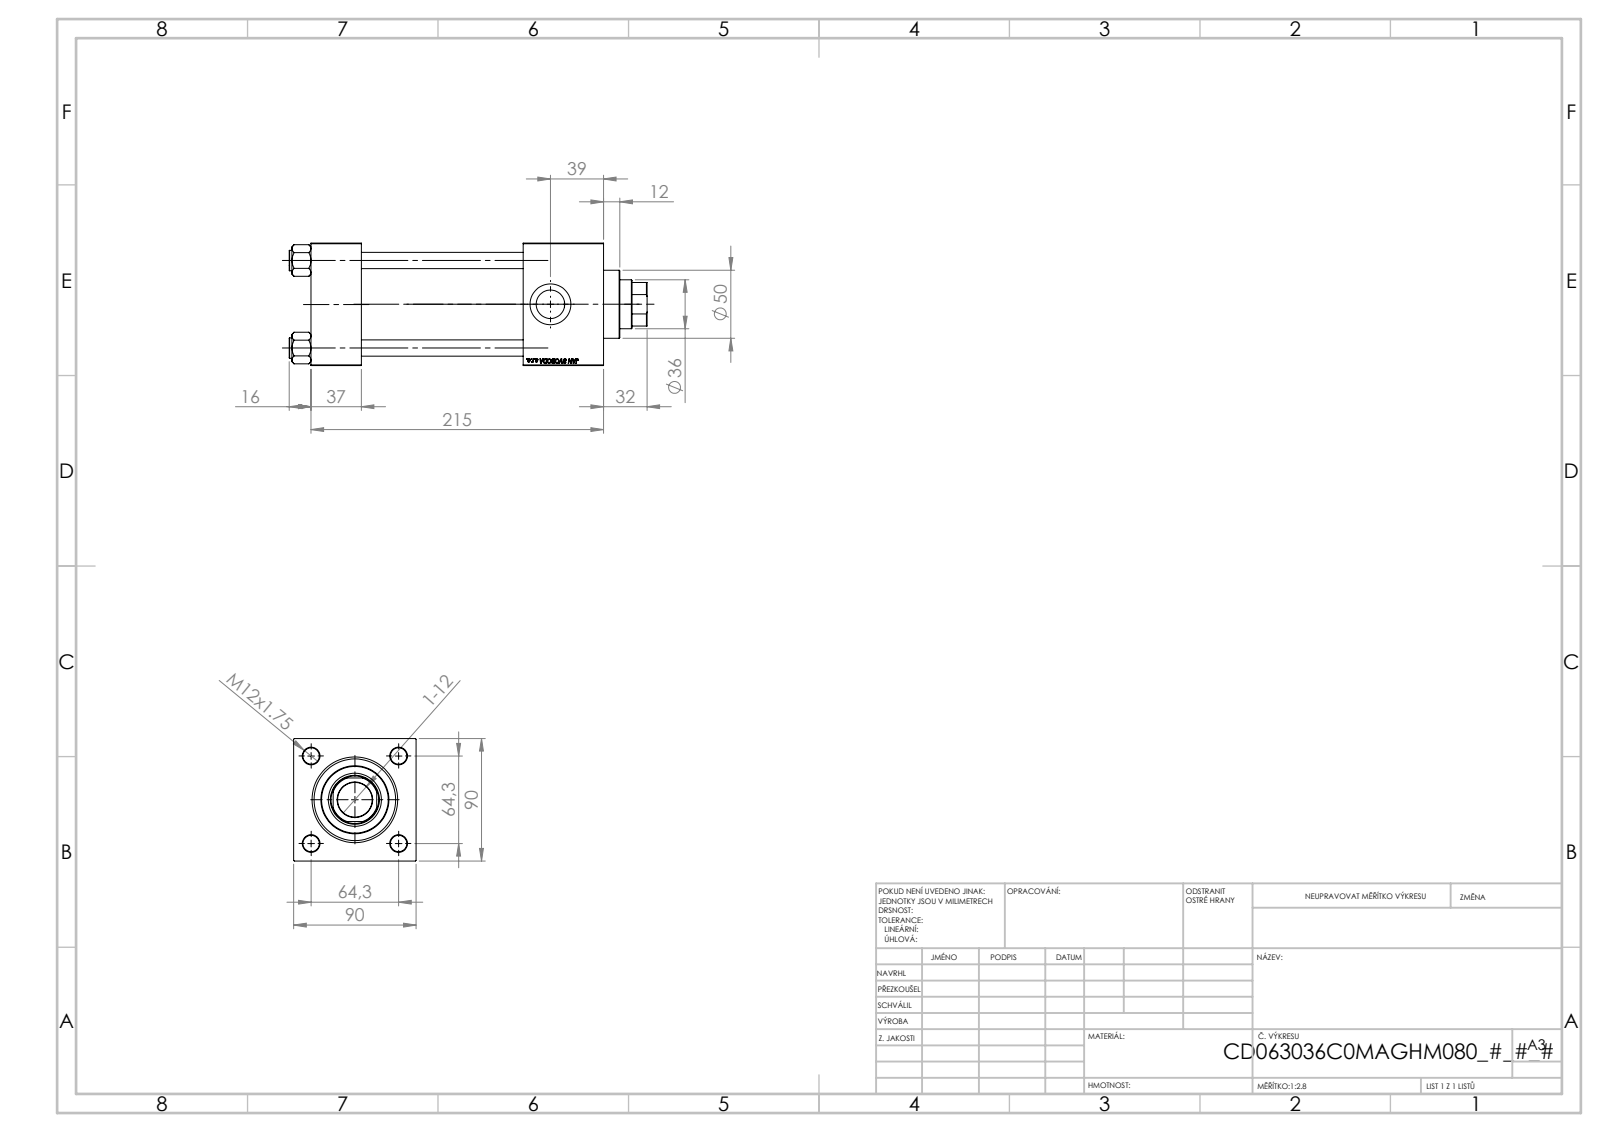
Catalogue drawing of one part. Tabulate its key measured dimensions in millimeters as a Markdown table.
| quantity | value |
| --- | --- |
| part name | V215CD_VC_C; V215CD_Body_C; V215CD_C_TYCINKA; NUT_M5_V215CD_C (+1 more) |
| STEP written by | SolidWorks 2019 (CONFIG_CONTROL_DESIGN) |
| units | millimeters |
| bodies | 11 solids, 1149 faces (526 planar, 87 cylindrical, 536 other) |
| overall size | 263 × 90 × 90 |
| volume | 1 093 000 mm³ |
| surface area | 224 953 mm² |
| round holes (diameter × count) | 12 × 4, 7 × 2, 20.96 × 2, 30 × 2, 25.5 × 1, 36 × 1, 39 × 1, 50 × 1, 60 × 1, 63 × 1 |
| round bosses / shafts (diameter × count) | 15 × 4, 69 × 1 |
| partial cylindrical surfaces (radius × count) | 17.5 × 1 |
| main face-to-face distances | 90, 37, 215, 178, 59, 156, 119, 186.3, 149.3, 30.3 |
| hole center spacings | 45.47, 64.3, 90.93 |
